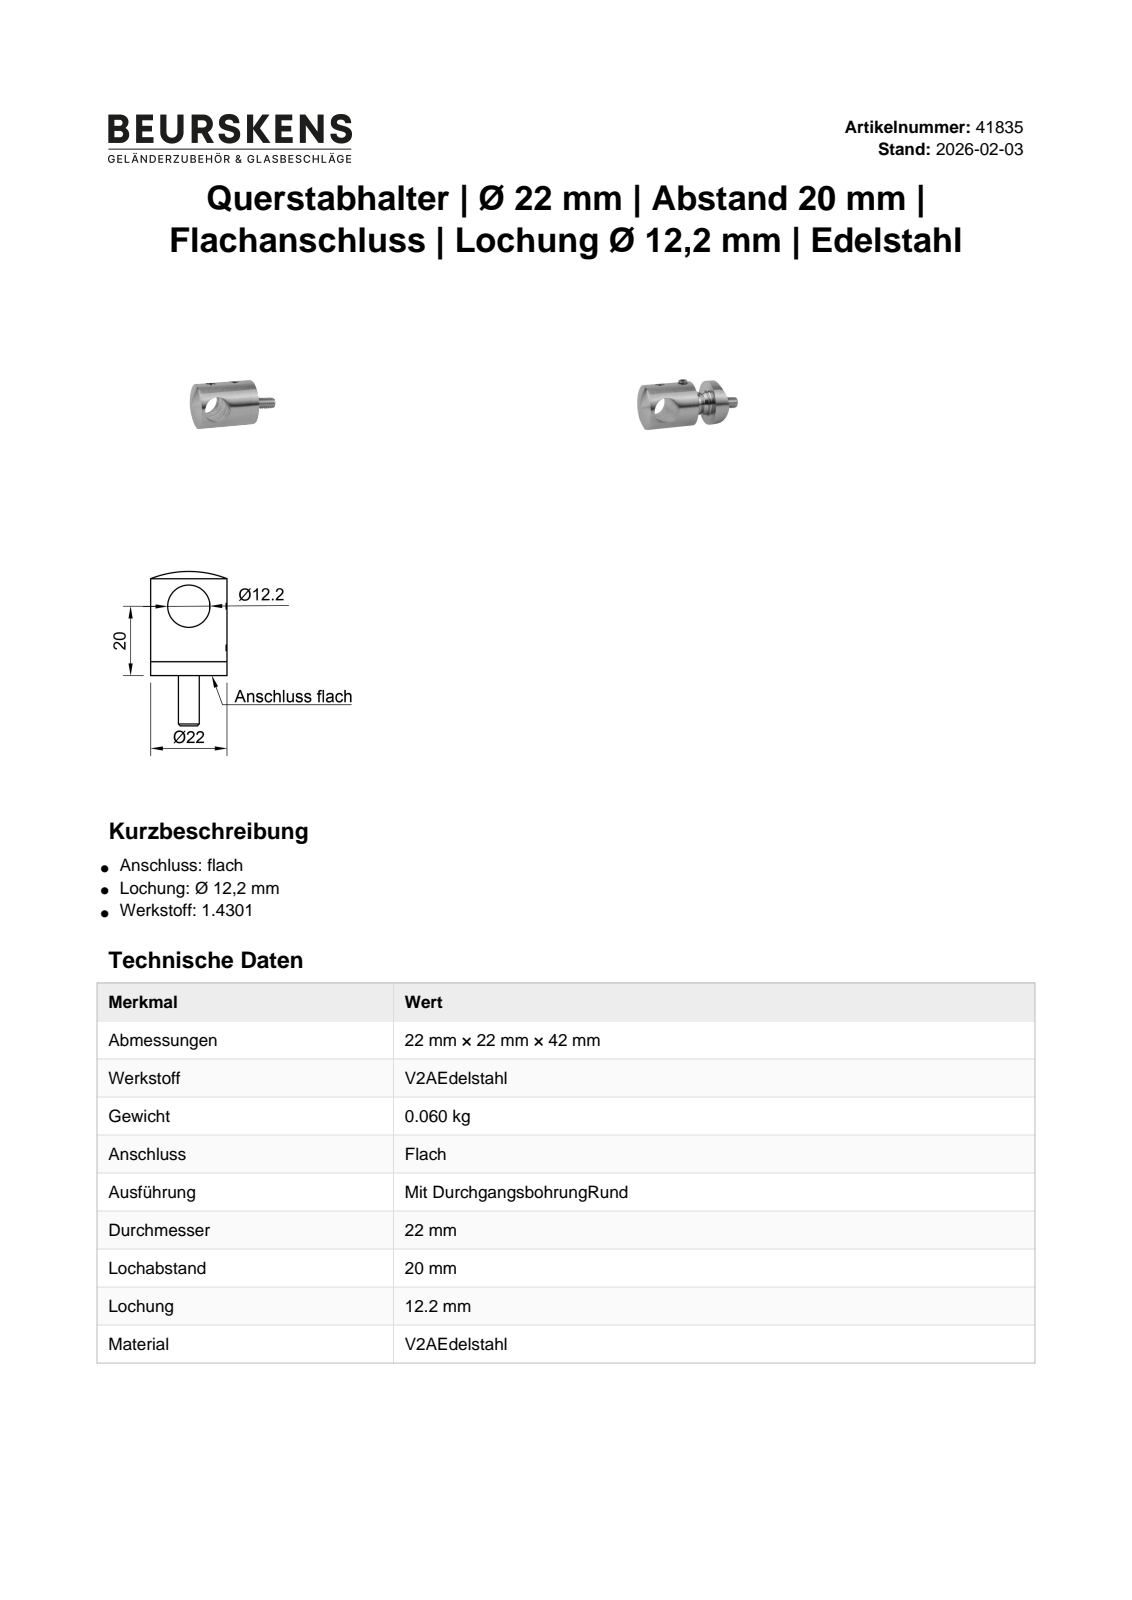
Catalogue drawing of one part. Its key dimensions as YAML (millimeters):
part_name: "41835 for customer; H-22-42.4ñ; socket countersunk head screw_din_DIN 7991 - M6 x 25 --- 18.7N; socket set screw flat point_din_DIN 913 - M5 x 5-N"
step_written_by: "SolidWorks 2020 (CONFIG_CONTROL_DESIGN)"
units: millimeters
bodies: {solids: 5, faces: 96, planar: 38, cylindrical: 26, other: 32}
overall_size: [44.48, 22, 22]
volume: 8506
surface_area: 5701
round_holes:
  - {diameter: 4, count: 2}
  - {diameter: 7, count: 1}
  - {diameter: 11.2, count: 1}
  - {diameter: 12.2, count: 1}
  - {diameter: 14, count: 1}
round_bosses_or_shafts:
  - {diameter: 5, count: 2}
  - {diameter: 22, count: 1}
  - {diameter: 12.8, count: 1}
  - {diameter: 11.57, count: 1}
  - {diameter: 6, count: 1}
face_to_face_distances: [4, 2, 10.51, 6.51, 9.5, 8.51, 13.5, 11.5, 2.99, 6]
hole_center_spacings: [12]
